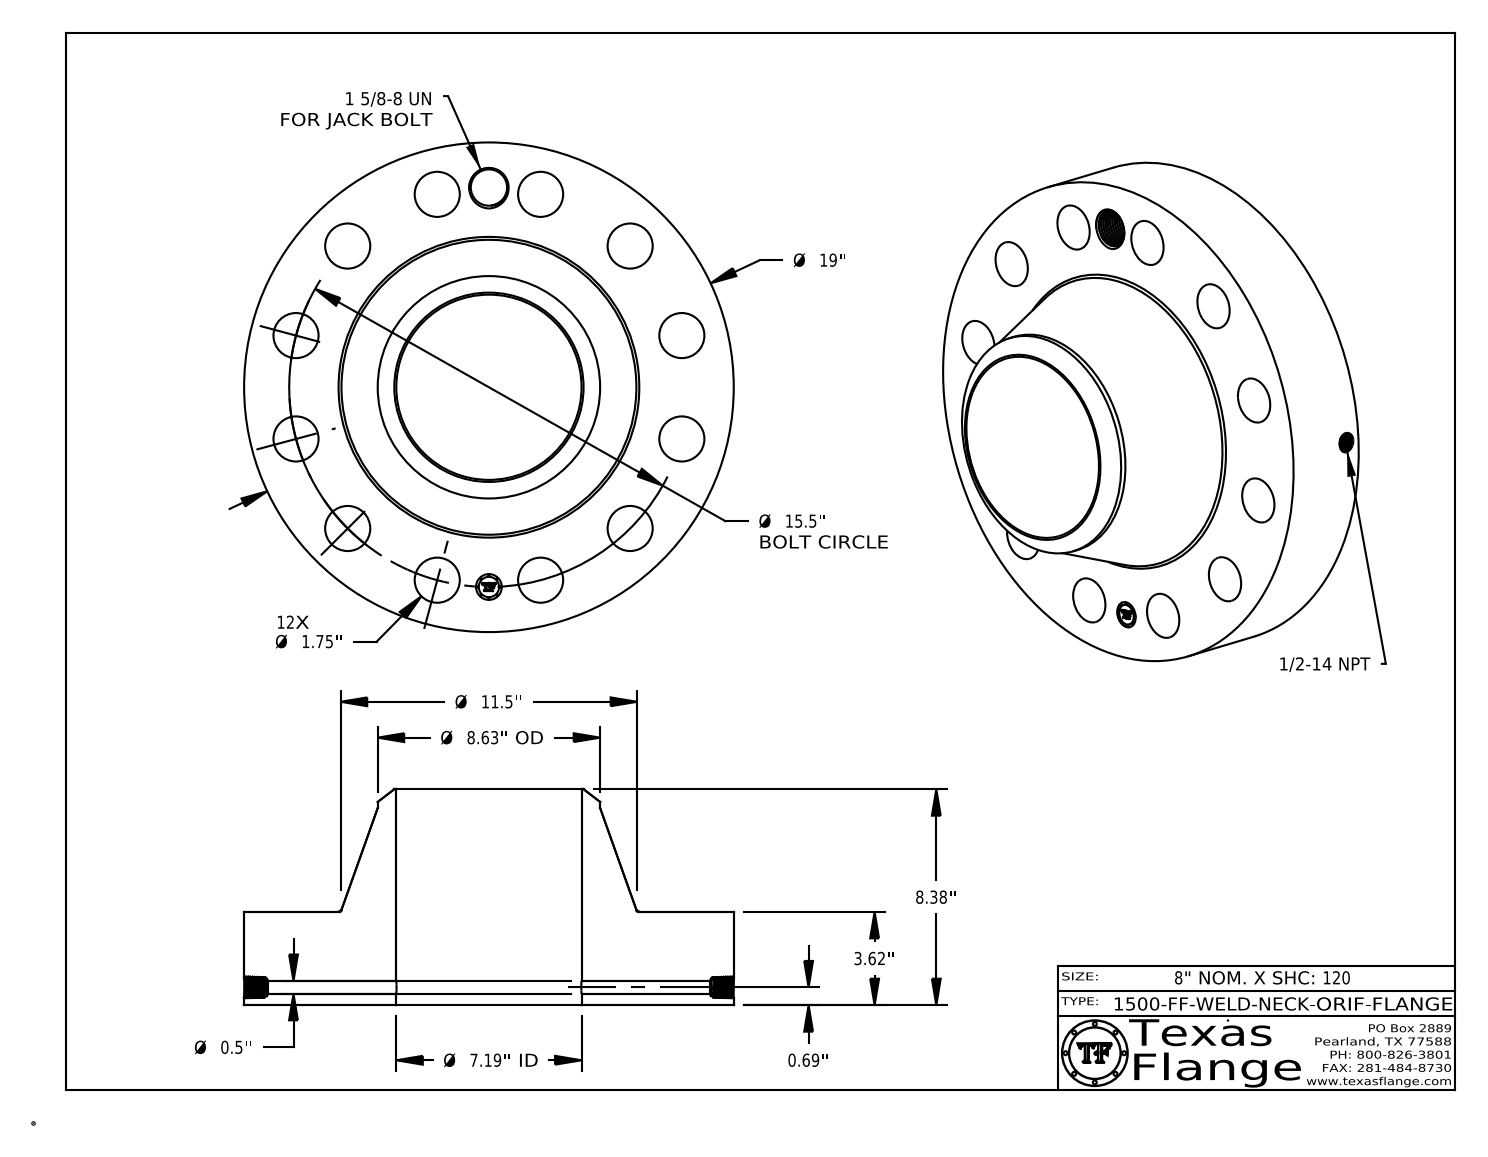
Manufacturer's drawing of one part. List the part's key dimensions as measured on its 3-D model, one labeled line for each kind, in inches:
Part name (STEP PRODUCT): 1500-FF-WELD-NECK
STEP written by: CATIA V5 STEP AP214 (AUTOMOTIVE_DESIGN)
Units: inches
Bodies: 1 solid, 858 faces (368 planar, 127 cylindrical, 363 other)
Overall size (bounding box): 19 × 19 × 8.38
Volume: 934.1 in³ · Surface area: 1 225 in²
Round holes (diameter × count): ⌀1.75 ×12, ⌀0.5 ×1, ⌀0.672 ×1, ⌀1 ×1, ⌀1.409 ×1, ⌀7.187 ×1
Round bosses / shafts (diameter × count): ⌀0.061 ×8, ⌀19 ×1, ⌀8.63 ×1, ⌀0.788 ×1
Main face-to-face distances: 3.62, 8.38, 4.76, 3.605, 0.015, 4.775, 0.298, 0.293, 0.054, 0.248
Hole centre spacings: 7.75, 13.423, 14.972, 4.011, 7.75, 10.96, 15.5, 2.023
